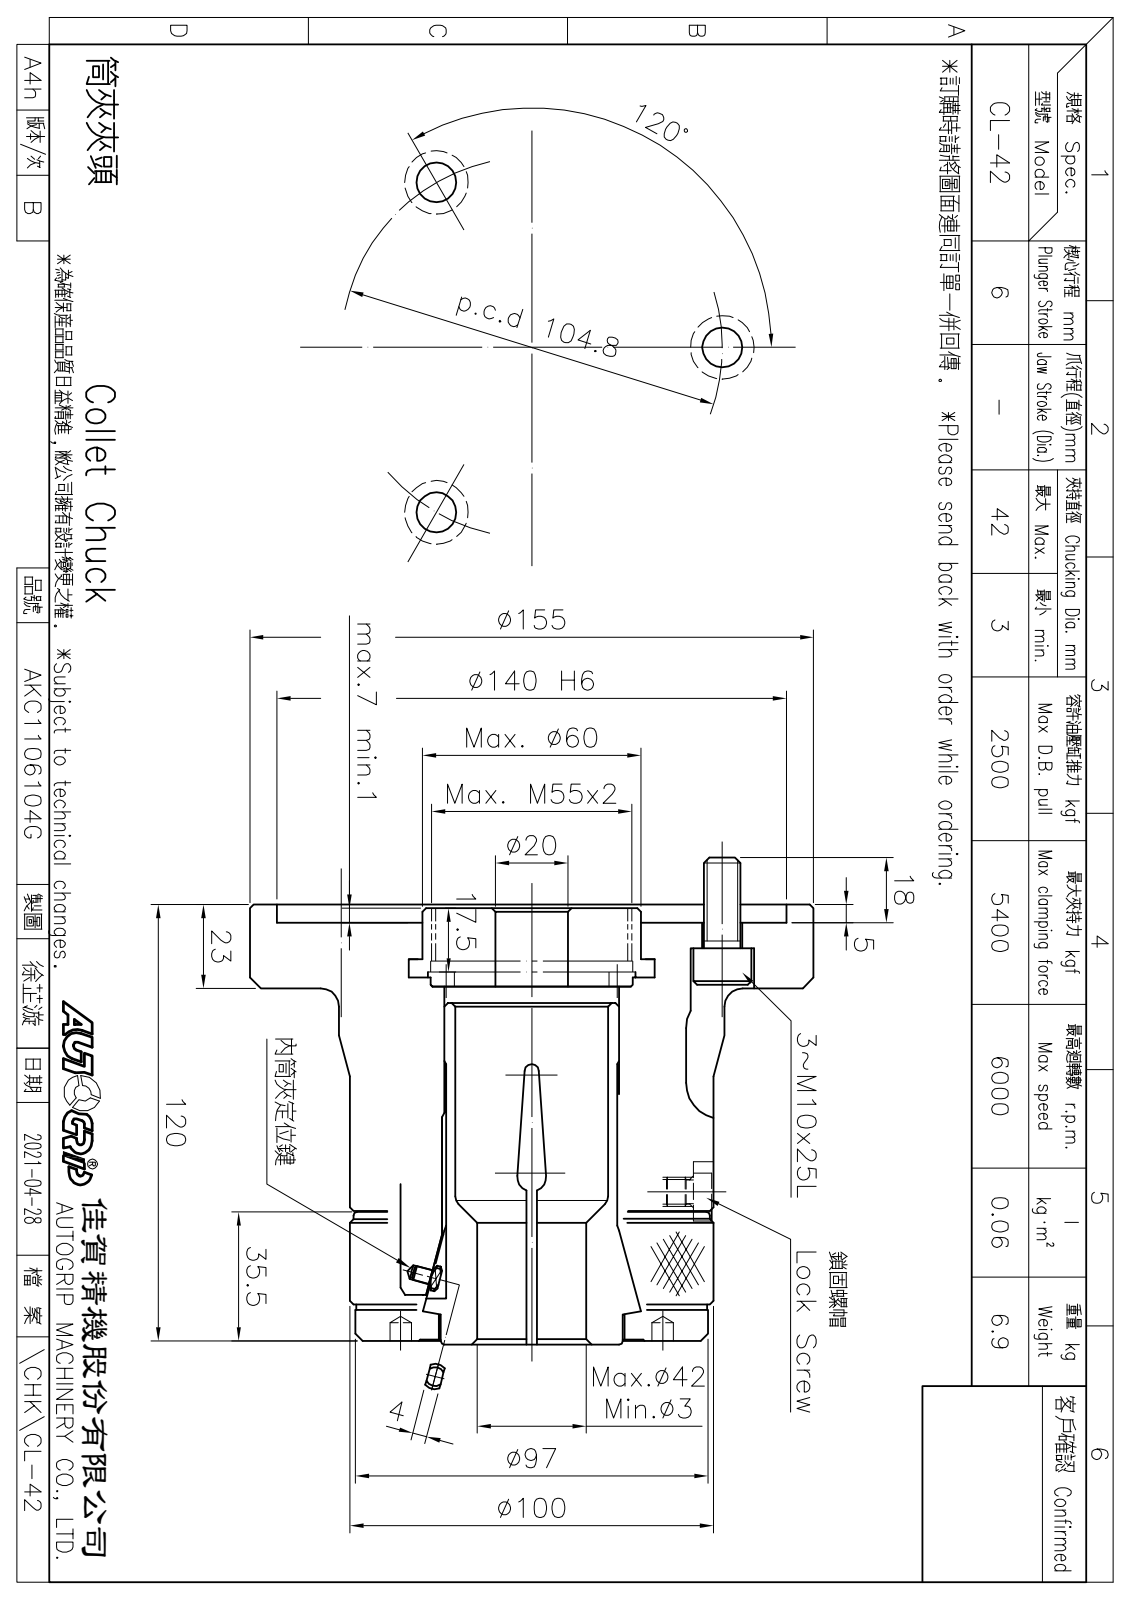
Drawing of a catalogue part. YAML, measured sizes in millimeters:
part_name: "CL-42外觀參考; CL-42內部; CL-42筒夾本體"
step_written_by: "SolidWorks 2011 (CONFIG_CONTROL_DESIGN)"
units: millimeters
bodies: {solids: 3, faces: 220, planar: 27, cylindrical: 91, other: 102}
overall_size: [155, 155, 120]
volume: 828868
surface_area: 169057
round_holes:
  - {diameter: 6, count: 5}
  - {diameter: 5, count: 3}
  - {diameter: 11, count: 3}
  - {diameter: 17.5, count: 3}
  - {diameter: 48, count: 1}
  - {diameter: 51, count: 1}
  - {diameter: 55, count: 1}
  - {diameter: 72, count: 1}
  - {diameter: 79.5, count: 1}
  - {diameter: 80, count: 1}
  - {diameter: 85, count: 1}
  - {diameter: 140, count: 1}
round_bosses_or_shafts:
  - {diameter: 155, count: 1}
  - {diameter: 106, count: 1}
  - {diameter: 100, count: 1}
  - {diameter: 97, count: 1}
  - {diameter: 84, count: 1}
  - {diameter: 60, count: 1}
partial_cylinders:
  - {radius: 10, count: 3}
face_to_face_distances: [18, 97, 115, 105.9, 87.9, 9.1, 26, 10, 9.5, 5]
hole_center_spacings: [15.44, 52.4, 58, 87.65, 90.76, 100.45, 102.02, 27.83]
